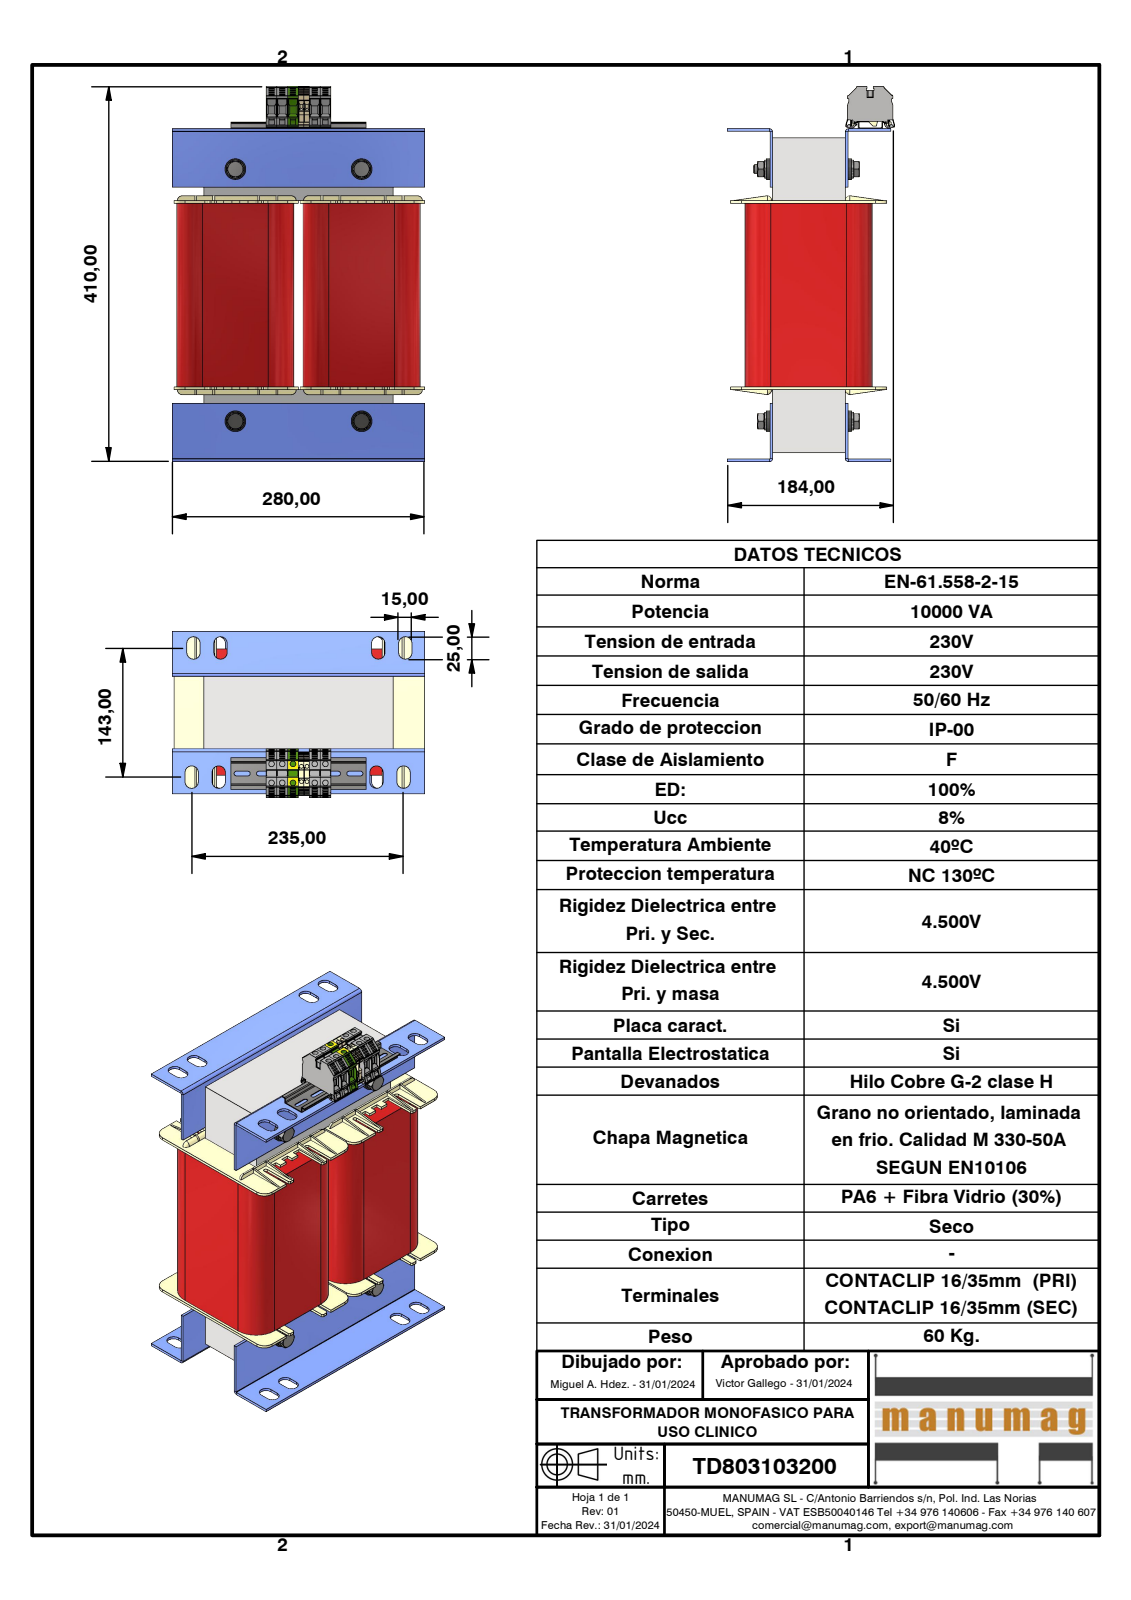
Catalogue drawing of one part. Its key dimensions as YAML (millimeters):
part_name: "TD803103200; UI350 x 210 - 80 (Rc70); UI 210_80_BOBINADO; RC 70 UI (+8 more)"
step_written_by: "Autodesk Inventor 2023 (AUTOMOTIVE_DESIGN)"
units: millimeters
bodies: {solids: 39, faces: 3760, planar: 2282, cylindrical: 1196, other: 282}
overall_size: [417.1, 327, 184.4]
volume: 10110000
surface_area: 1340000
round_holes:
  - {diameter: 6.3, count: 10}
  - {diameter: 4.3, count: 4}
  - {diameter: 8.38, count: 4}
  - {diameter: 10.5, count: 4}
  - {diameter: 14, count: 4}
  - {diameter: 16, count: 4}
  - {diameter: 2.4, count: 2}
  - {diameter: 2.5, count: 2}
  - {diameter: 2.75, count: 2}
  - {diameter: 2.95, count: 2}
round_bosses_or_shafts:
  - {diameter: 23, count: 4}
  - {diameter: 20, count: 4}
  - {diameter: 15.4, count: 4}
  - {diameter: 14.7, count: 4}
  - {diameter: 10, count: 4}
  - {diameter: 9.19, count: 4}
partial_cylinders:
  - {radius: 0.3, count: 263}
  - {radius: 0.25, count: 32}
  - {radius: 7.5, count: 32}
  - {radius: 2, count: 27}
  - {radius: 1, count: 18}
  - {radius: 0.5, count: 13}
  - {radius: 2.6, count: 12}
  - {radius: 2.5, count: 8}
face_to_face_distances: [3, 140, 80, 70, 26.5, 83, 25.58, 113.5, 0.92, 77]
hole_center_spacings: [11.9, 24.14, 21, 36, 41.68, 47.9, 52.3, 6.1]
